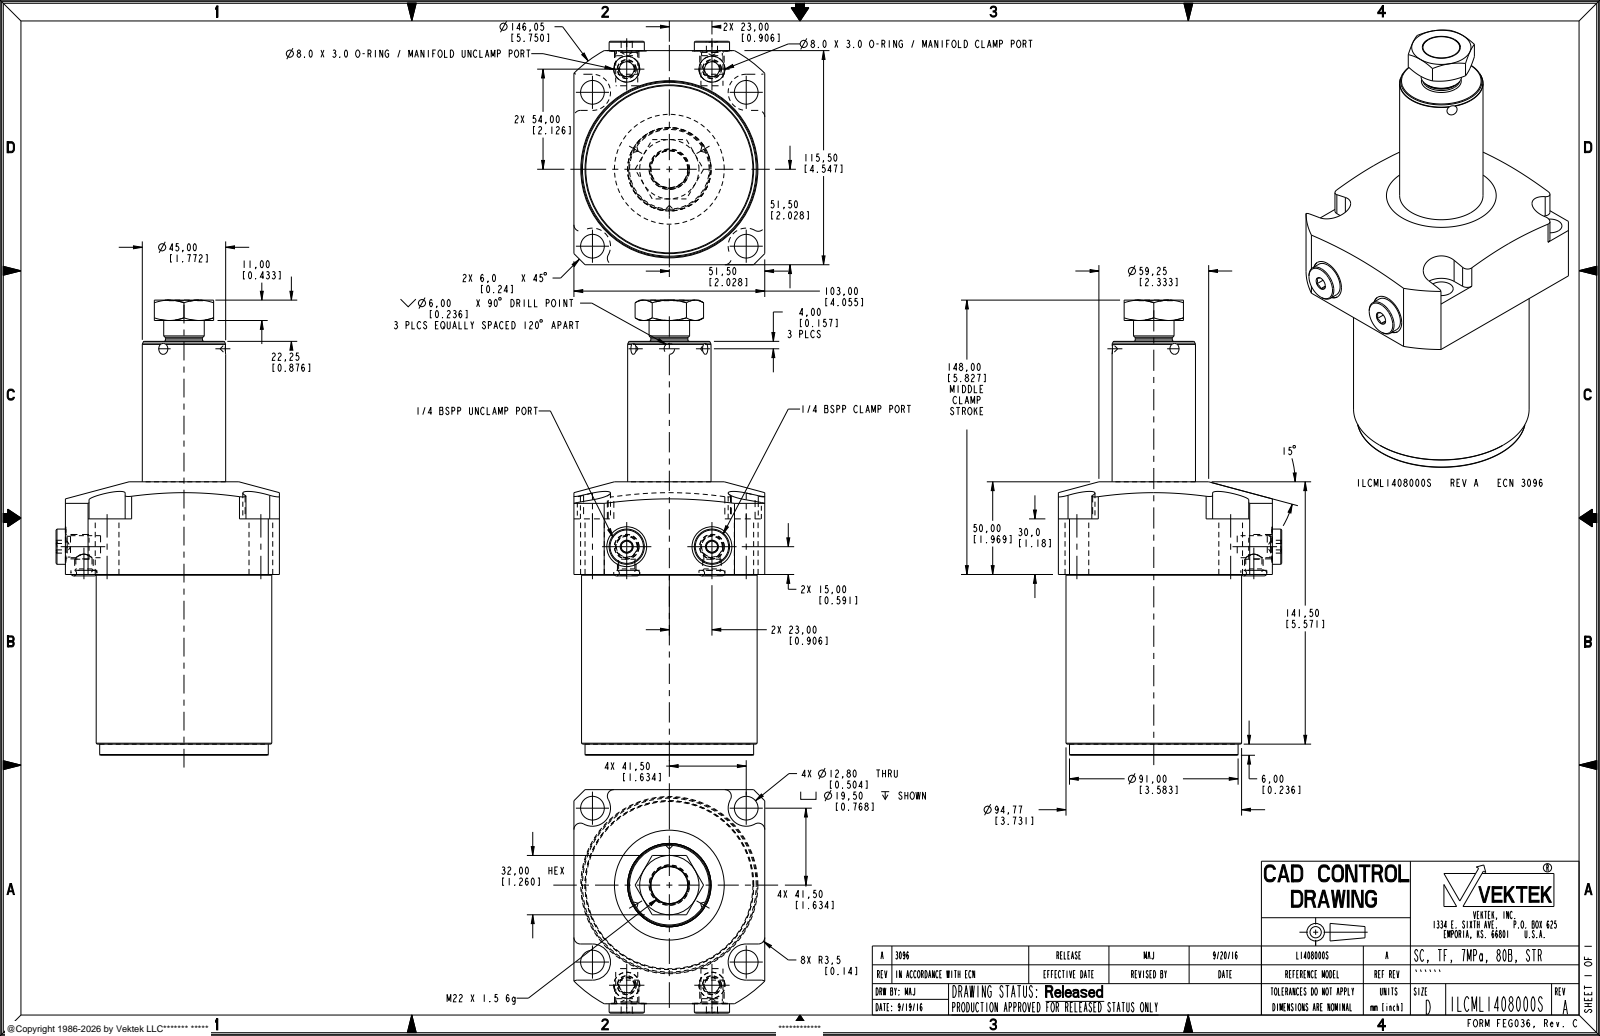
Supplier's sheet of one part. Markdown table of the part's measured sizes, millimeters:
| quantity | value |
| --- | --- |
| part name | ILCML1408000S |
| STEP written by | PRO/ENGINEER BY PARAMETRIC TECHNOLOGY CORPORATION, 2013320 (AUTOMOTIVE_DESIGN) |
| units | millimeters |
| bodies | 3 solids, 207 faces (68 planar, 70 cylindrical, 69 other) |
| overall size | 245.5 × 120.55 × 103 |
| volume | 1 324 000 mm³ |
| surface area | 93 529 mm² |
| round holes (diameter × count) | 12.8 × 4, 6 × 2, 8.75 × 2, 11.89 × 2, 14 × 2, 21.5 × 2, 20.5 × 1 |
| round bosses / shafts (diameter × count) | 19 × 2, 13.16 × 2, 11.2 × 2, 10 × 2, 94.77 × 1, 91 × 1, 45 × 1, 21.87 × 1 |
| partial cylindrical surfaces (radius × count) | 3.5 × 8, 9.75 × 4, 73.03 × 1 |
| main face-to-face distances | 103, 97.5, 115.5, 147.5, 50, 223.25, 125.75, 75.75, 127.5, 30 |
| hole center spacings | 58.69, 83, 22.33, 46, 65.7, 97.28, 115.24, 117.38 |
